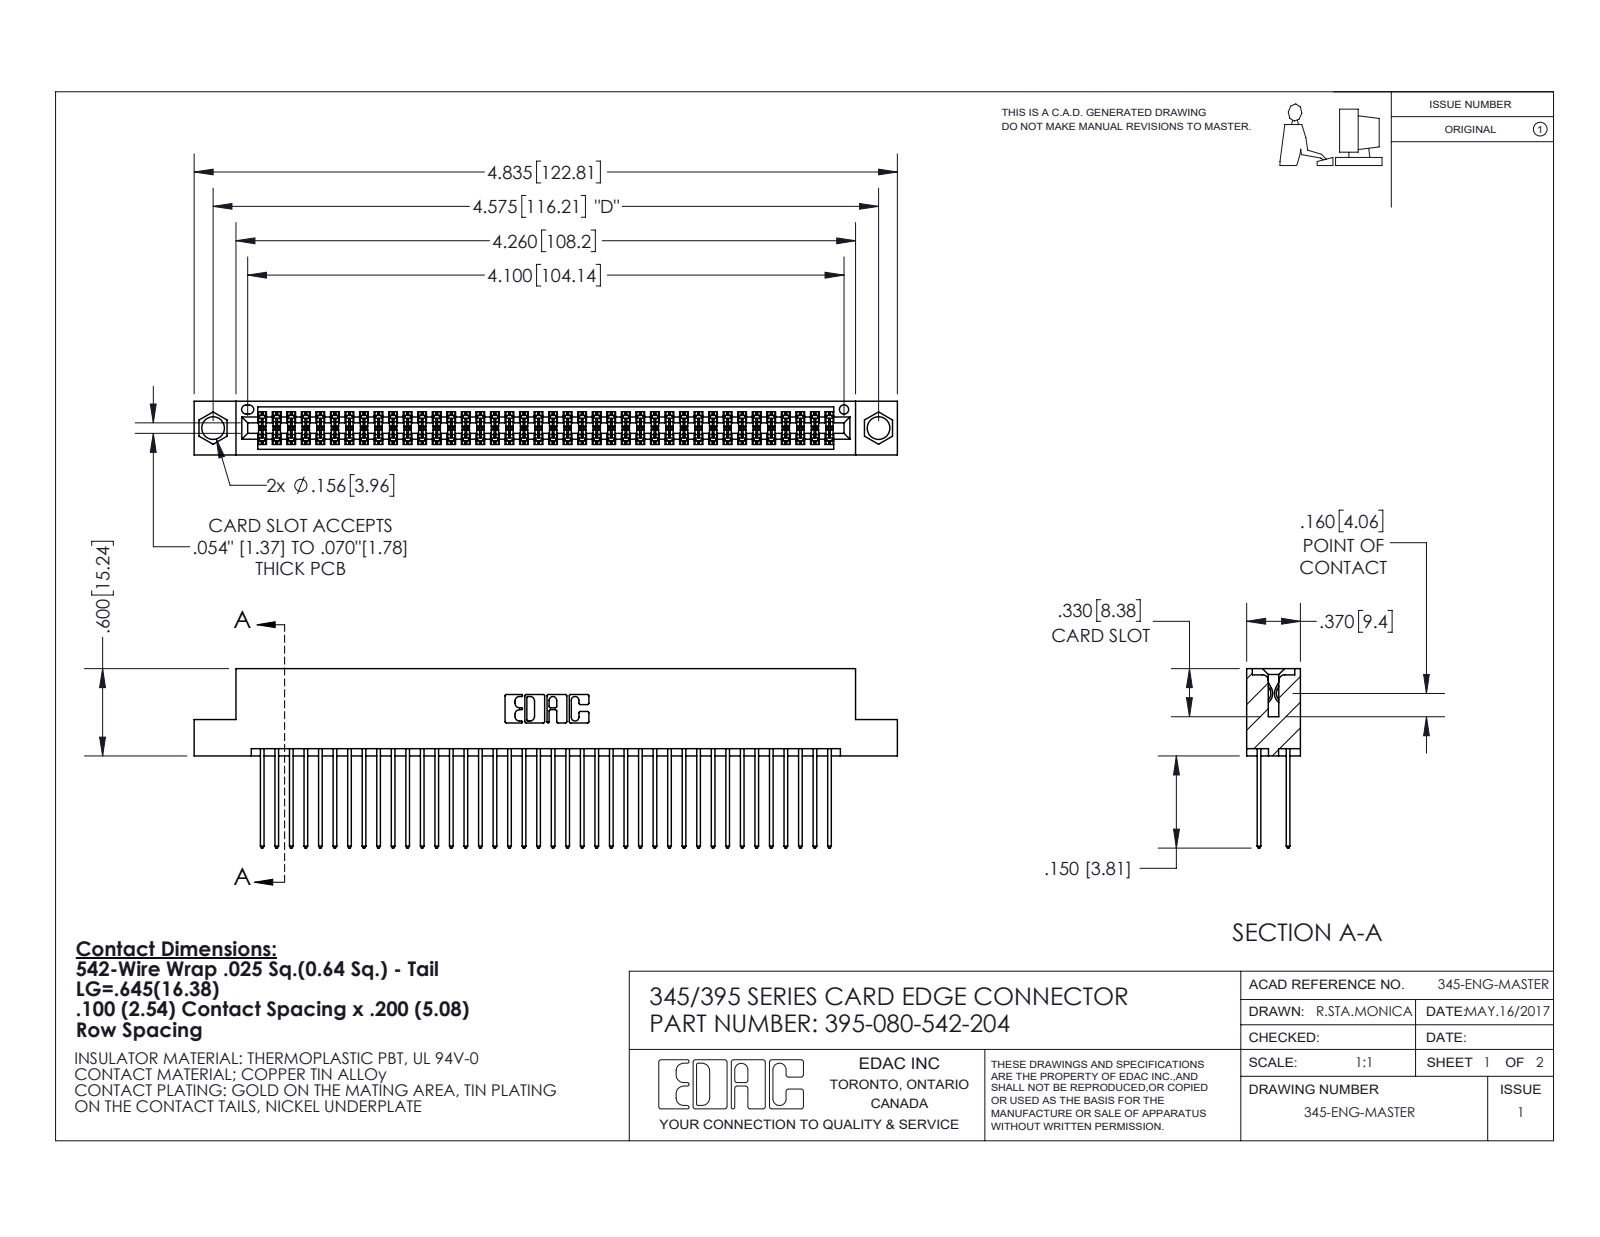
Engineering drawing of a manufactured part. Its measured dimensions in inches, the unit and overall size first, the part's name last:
Units: inches
Overall size (bounding box): 4.835 × 1.232 × 0.37
Round holes (diameter × count): ⌀0.156 ×2, ⌀0.064 ×1
Partial cylindrical surfaces — rounded edges, fillets, slot ends (radius × count): R0.006 ×120, R0.01 ×80, R0.01 ×22, R0.007 ×6, R0.031 ×6, R0.026 ×3, R0.014 ×2, R0.019 ×2
Main face-to-face distances: 0.298, 0.072, 0.2, 0.098, 0.272, 0.025, 0.37, 0.225, 0.175, 0.149
Hole centre spacings: 0.27, 4.339, 4.575
Volume: 0.743 in³ · Surface area: 30.31 in²
Bodies: 81 solids, 4140 faces (2734 planar, 1406 cylindrical, 0 other)
Part name (STEP PRODUCT): 345 Part_Flush Mounting Lugs - 0.156 Dia-TI; 395-080-542-204; 345-292-001_345-293-142
STEP written by: SolidWorks 2020 (CONFIG_CONTROL_DESIGN)
